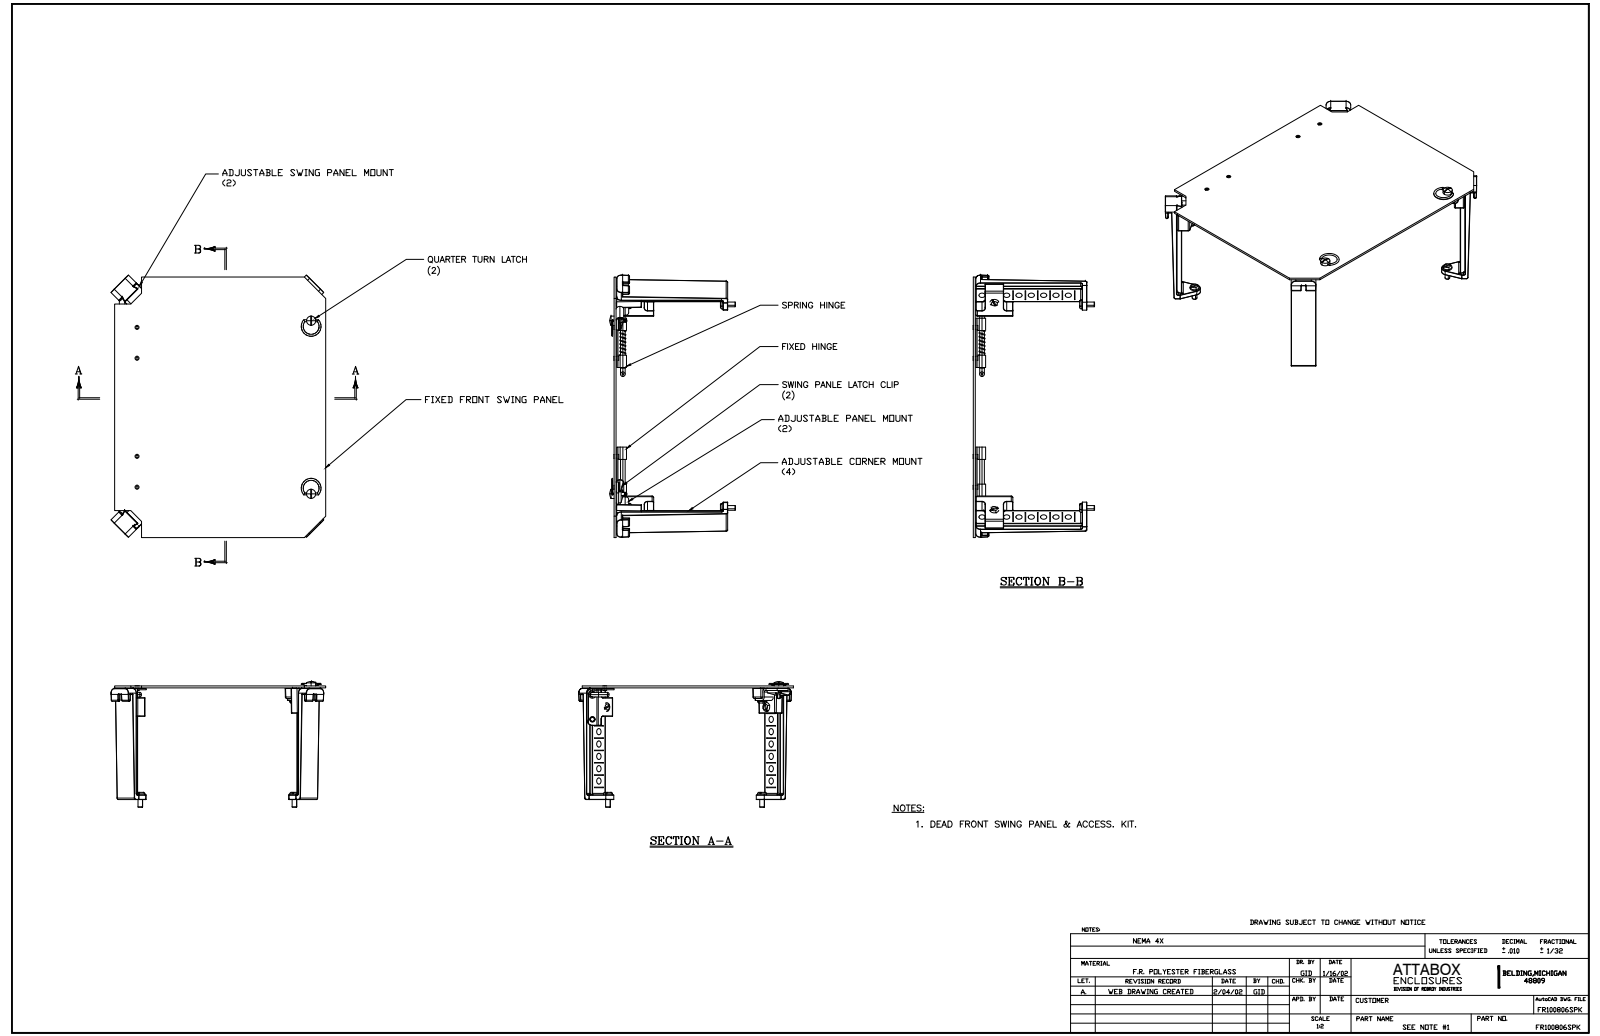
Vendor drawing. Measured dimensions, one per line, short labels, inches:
name: FR100806SPK
written by: SolidWorks 2019 (AUTOMOTIVE_DESIGN)
unit: in
bodies: 48 solids, 1805 faces (834 planar, 477 cylindrical, 494 other)
size: 10.622 × 8.716 × 5.181
volume: 15.95 in³; area: 310.5 in²
holes: 36× ⌀0.25, 6× ⌀0.156, 6× ⌀0.253, 4× ⌀0.05, 4× ⌀0.14, 4× ⌀0.144, 4× ⌀0.217, 4× ⌀0.22, 3× ⌀0.312, 2× ⌀0.153, 2× ⌀0.197, 2× ⌀0.35
bosses: 10× ⌀0.19, 6× ⌀0.373, 6× ⌀0.246, 5× ⌀0.16, 4× ⌀0.433, 4× ⌀0.315, 4× ⌀0.079, 3× ⌀0.187
rounds: 214× R0.01, 44× R0.06, 12× R0.063, 8× R0.025, 8× R0.13, 6× R0.062, 4× R0.049, 4× R0.125
face distances: 0.08, 11.295, 0.08, 0.166, 0.086, 0.161, 6.855, 4.441, 5.44, 5.855
hole spacings: 1.5, 0.5, 1, 1.732, 2.061, 2, 1.414, 2.45
